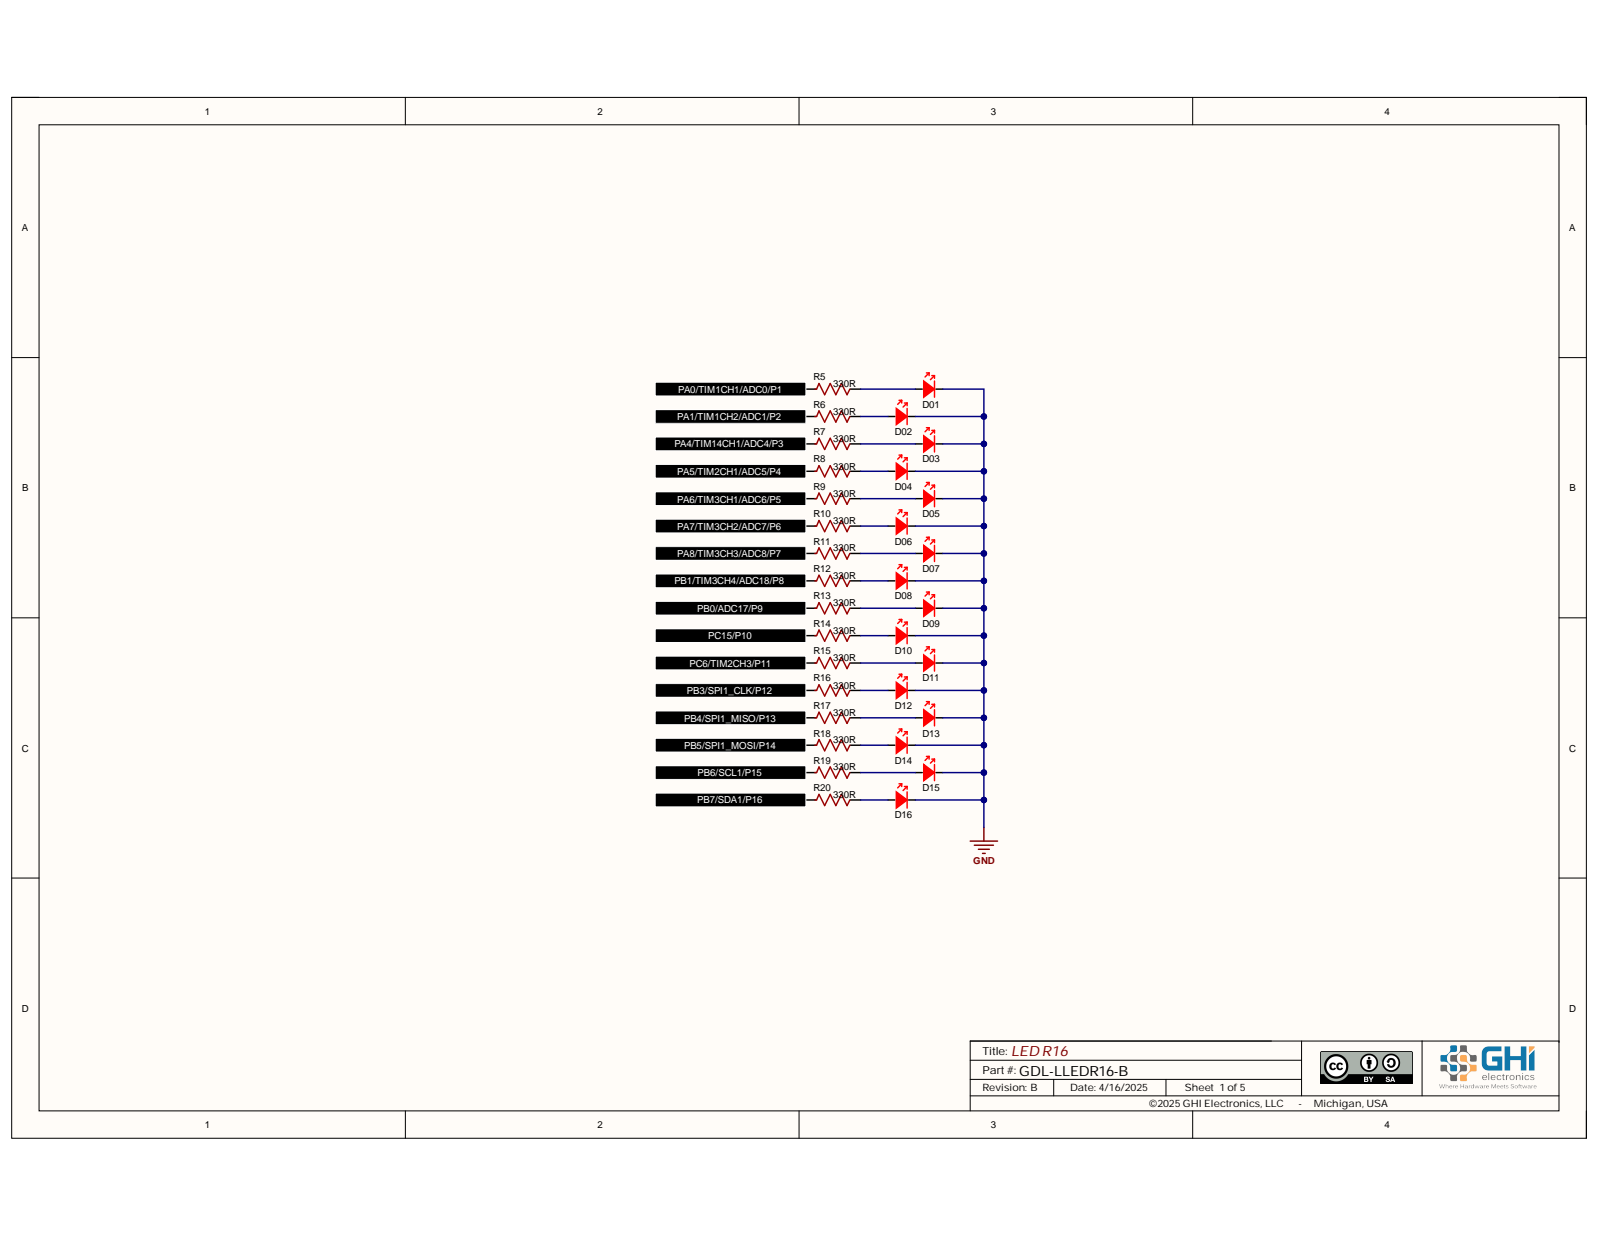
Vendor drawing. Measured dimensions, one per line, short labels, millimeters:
name: PCB; Board; STAT1; 0603 LED Green (+5 more)
written by: Open CASCADE 7.5 (AUTOMOTIVE_DESIGN)
unit: mm
bodies: 271 solids, 3759 faces (2735 planar, 460 cylindrical, 564 other)
size: 32 × 32 × 6.92
volume: 1 679 mm³; area: 3 022 mm²
holes: 4× ⌀3, 2× ⌀1.02
rounds: 46× R0.15, 35× R0.12, 34× R0.17, 34× R0.18, 34× R0.18, 4× R3.5
face distances: 1.6, 32, 1.9, 1.63, 0.55, 0.45, 2.53, 28.12, 0.9, 31.45
hole spacings: 25, 35.36, 2.54, 5.16, 7.56, 17.85, 20.37, 27.47
